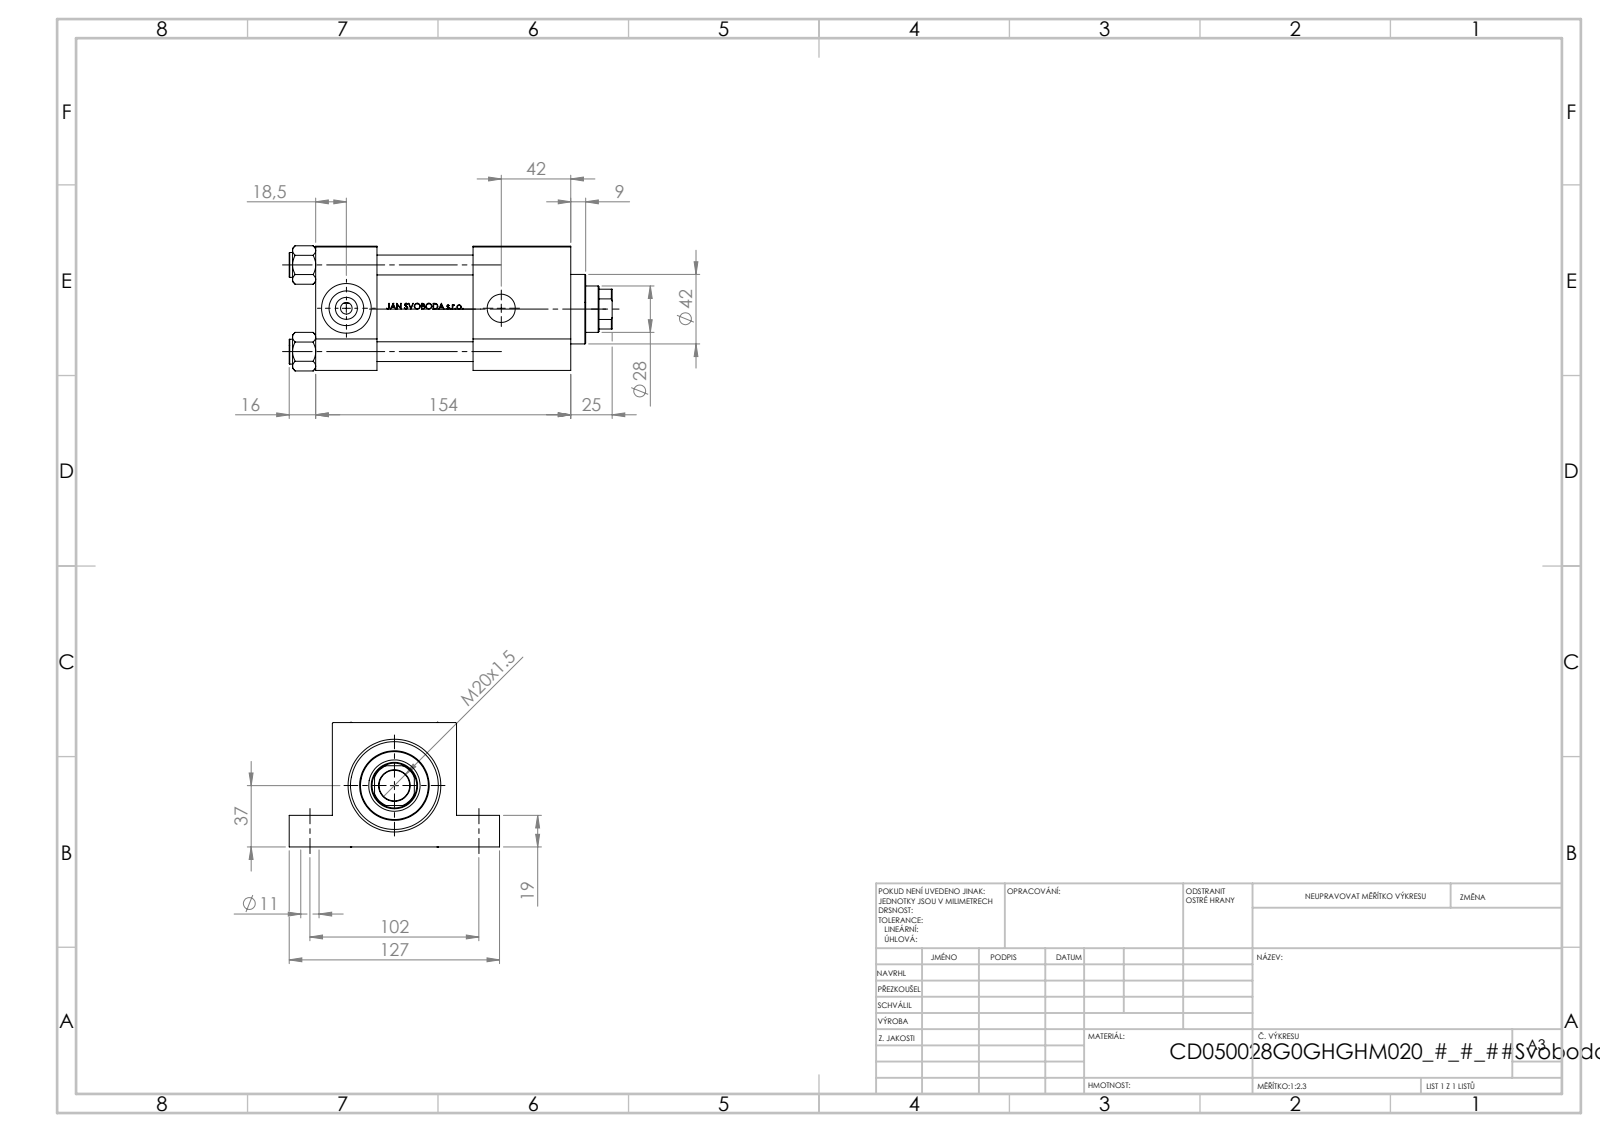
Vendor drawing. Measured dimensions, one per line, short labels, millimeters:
name: V215CD_VC_G; V215CD_NUT_M5_G; V215CD_G_TYCINKA; V215CD_VCP_G (+1 more)
written by: SolidWorks 2019 (CONFIG_CONTROL_DESIGN)
unit: mm
bodies: 11 solids, 1087 faces (431 planar, 124 cylindrical, 532 other)
size: 195 × 127 × 75.54
volume: 768 066 mm³; area: 163 198 mm²
holes: 4× ⌀11, 4× ⌀12, 2× ⌀7, 2× ⌀20.96, 1× ⌀17, 1× ⌀18.5, 1× ⌀28, 1× ⌀30, 1× ⌀31, 1× ⌀41, 1× ⌀50, 1× ⌀53
bosses: 4× ⌀15, 1× ⌀56, 1× ⌀42
rounds: 1× R13.5
face distances: 75, 37, 154, 117, 19, 56, 95, 58, 59, 26
hole spacings: 52.3, 36.63, 37.34, 73.96, 102, 112, 151.49, 93.5
